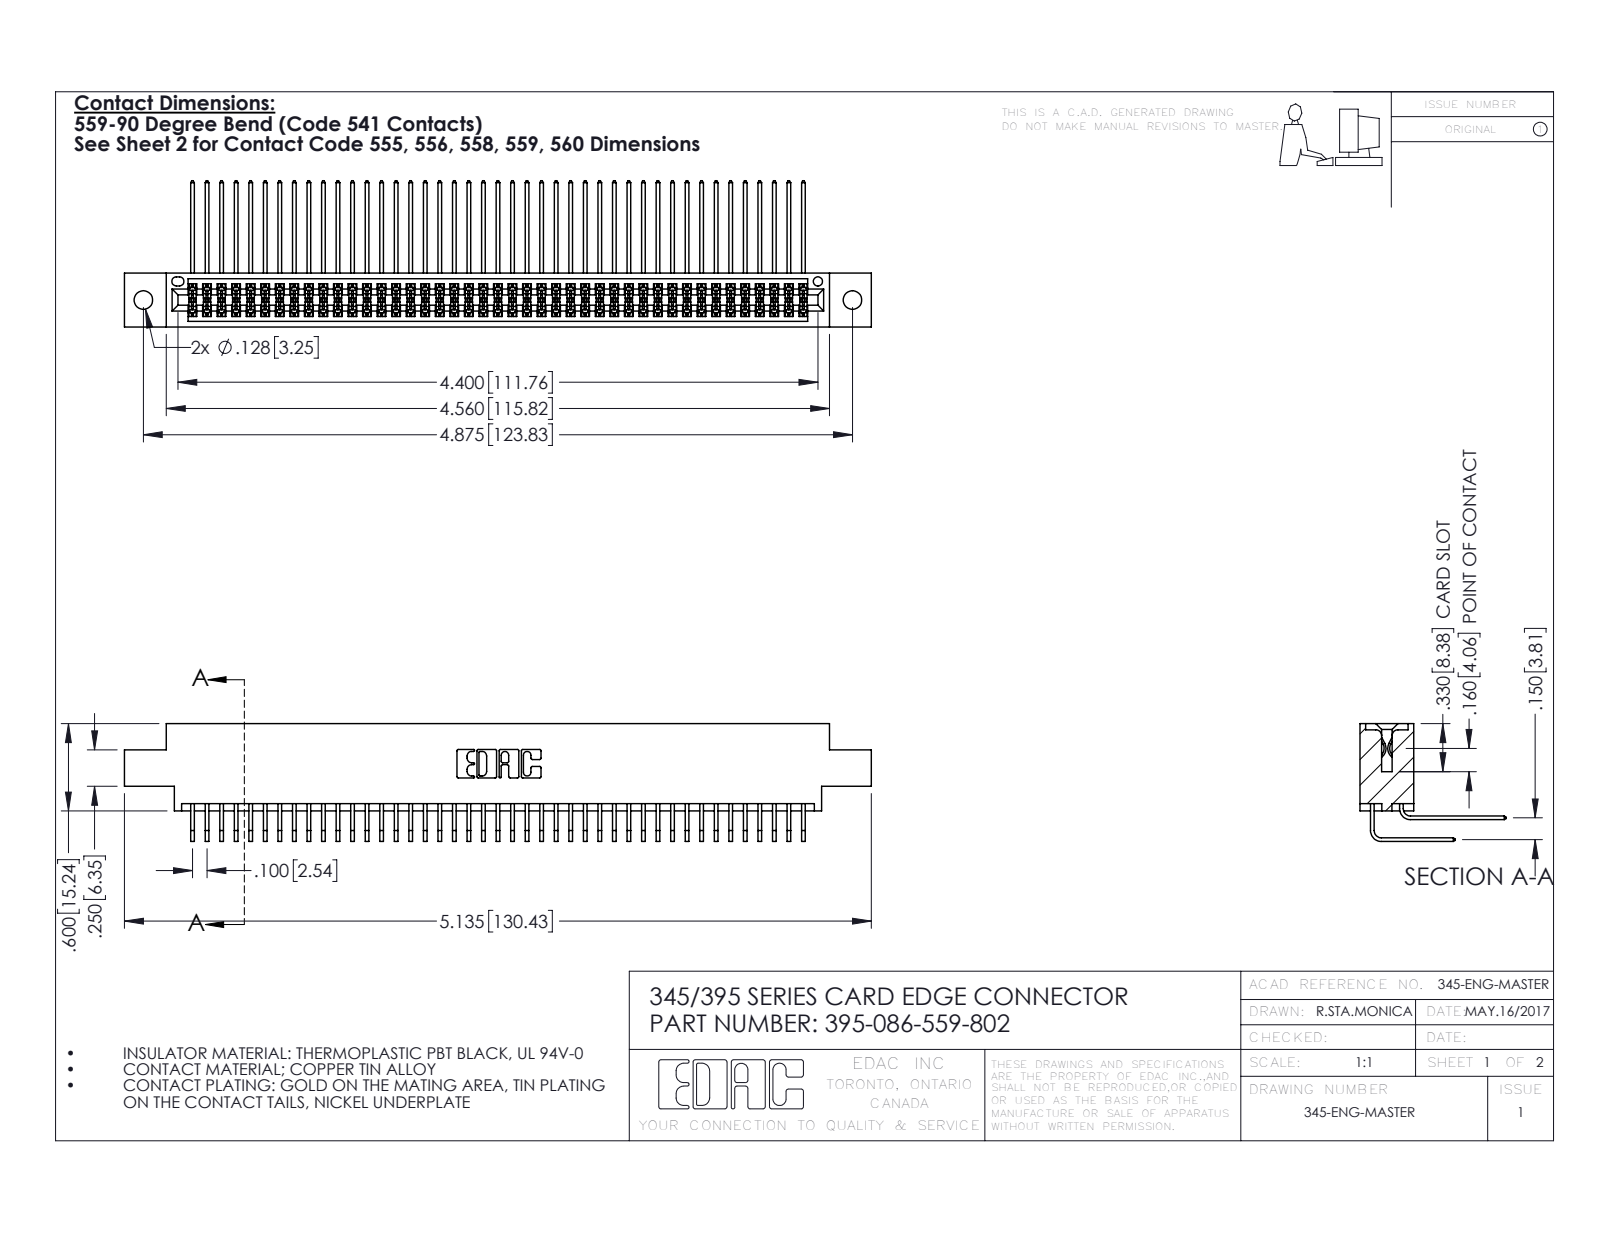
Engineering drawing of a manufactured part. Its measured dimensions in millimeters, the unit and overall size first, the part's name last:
Units: millimetres
Overall size (bounding box): 130.4 × 25.5 × 20.5
Round holes (diameter × count): ⌀3.3 ×2, ⌀1.6 ×1
Partial cylindrical surfaces — rounded edges, fillets, slot ends (radius × count): R0.2 ×129, R0.3 ×22, R0.2 ×6, R0.8 ×6, R0.7 ×3, R0.4 ×2, R0.5 ×2, R0.6 ×2
Main face-to-face distances: 1.8, 7.6, 9.4, 5.1, 2.5, 6.9, 0.6, 5.7, 4.4, 3.8
Hole centre spacings: 6.9, 117.8, 123.8
Volume: 13 000 mm³ · Surface area: 21 480 mm²
Bodies: 87 solids, 4602 faces (3094 planar, 1508 cylindrical, 0 other)
Part name (STEP PRODUCT): 395-086-559-802; 345 Part_0.170 Offset - 0.128 Dia; 345-292-001_558 559 Tail - 1; 345-292-001_559 Tail - 2
STEP written by: SolidWorks 2016 (CONFIG_CONTROL_DESIGN)
